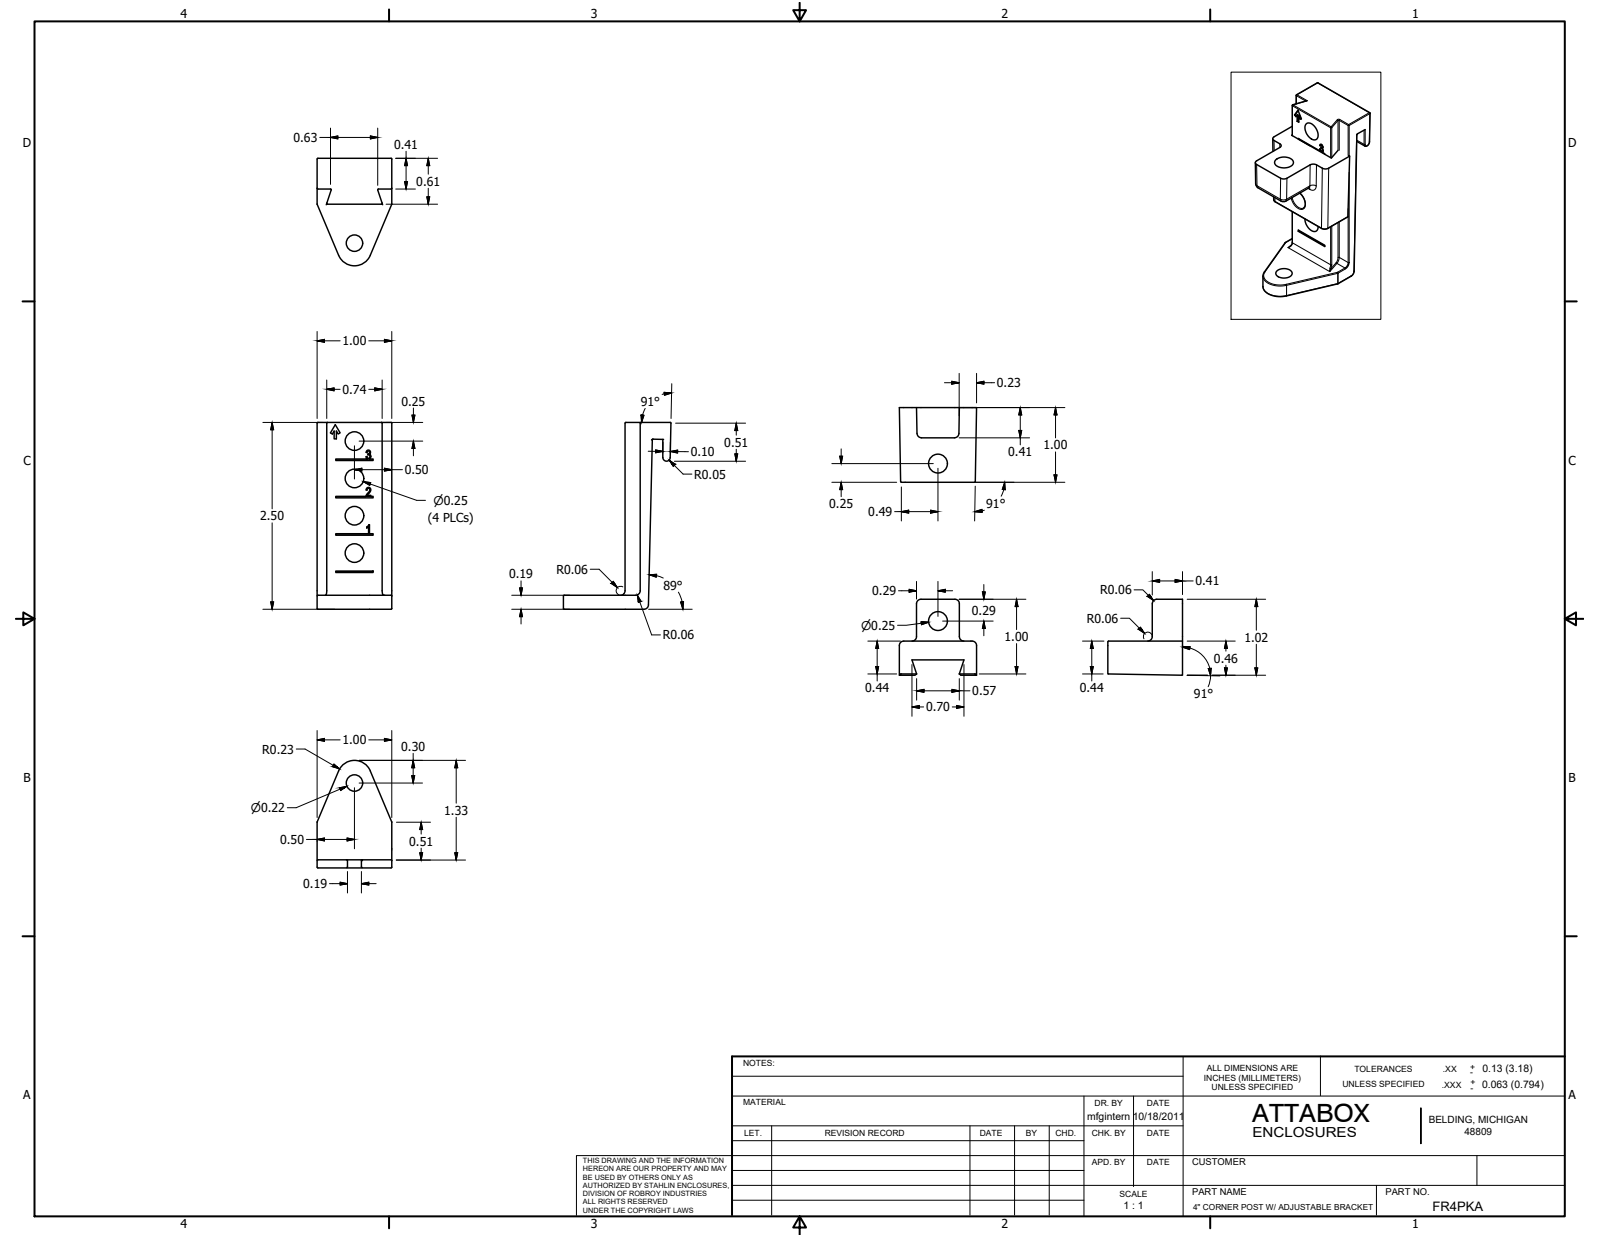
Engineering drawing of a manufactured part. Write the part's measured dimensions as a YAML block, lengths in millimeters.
part_name: "FR4PKA"
step_written_by: "SolidWorks 2019 (AUTOMOTIVE_DESIGN)"
units: millimeters
bodies: {solids: 24, faces: 1024, planar: 440, cylindrical: 300, other: 284}
overall_size: [166.5, 166.5, 68.7]
volume: 86920
surface_area: 48100
round_holes:
  - {diameter: 6.4, count: 16}
  - {diameter: 6.4, count: 8}
  - {diameter: 5.5, count: 4}
  - {diameter: 5.6, count: 4}
round_bosses_or_shafts:
  - {diameter: 4.8, count: 12}
  - {diameter: 9.5, count: 8}
  - {diameter: 11, count: 4}
  - {diameter: 8, count: 4}
partial_cylinders:
  - {radius: 0.3, count: 172}
  - {radius: 1.5, count: 52}
  - {radius: 1.2, count: 4}
  - {radius: 5.8, count: 4}
face_to_face_distances: [179.2, 76.9, 102.3, 5.2, 82, 107.4, 184.3, 25.4, 39.8, 81.7]
hole_center_spacings: [12.7, 25.4, 1.6, 11.1, 23.8, 36.5, 38.1, 108]
